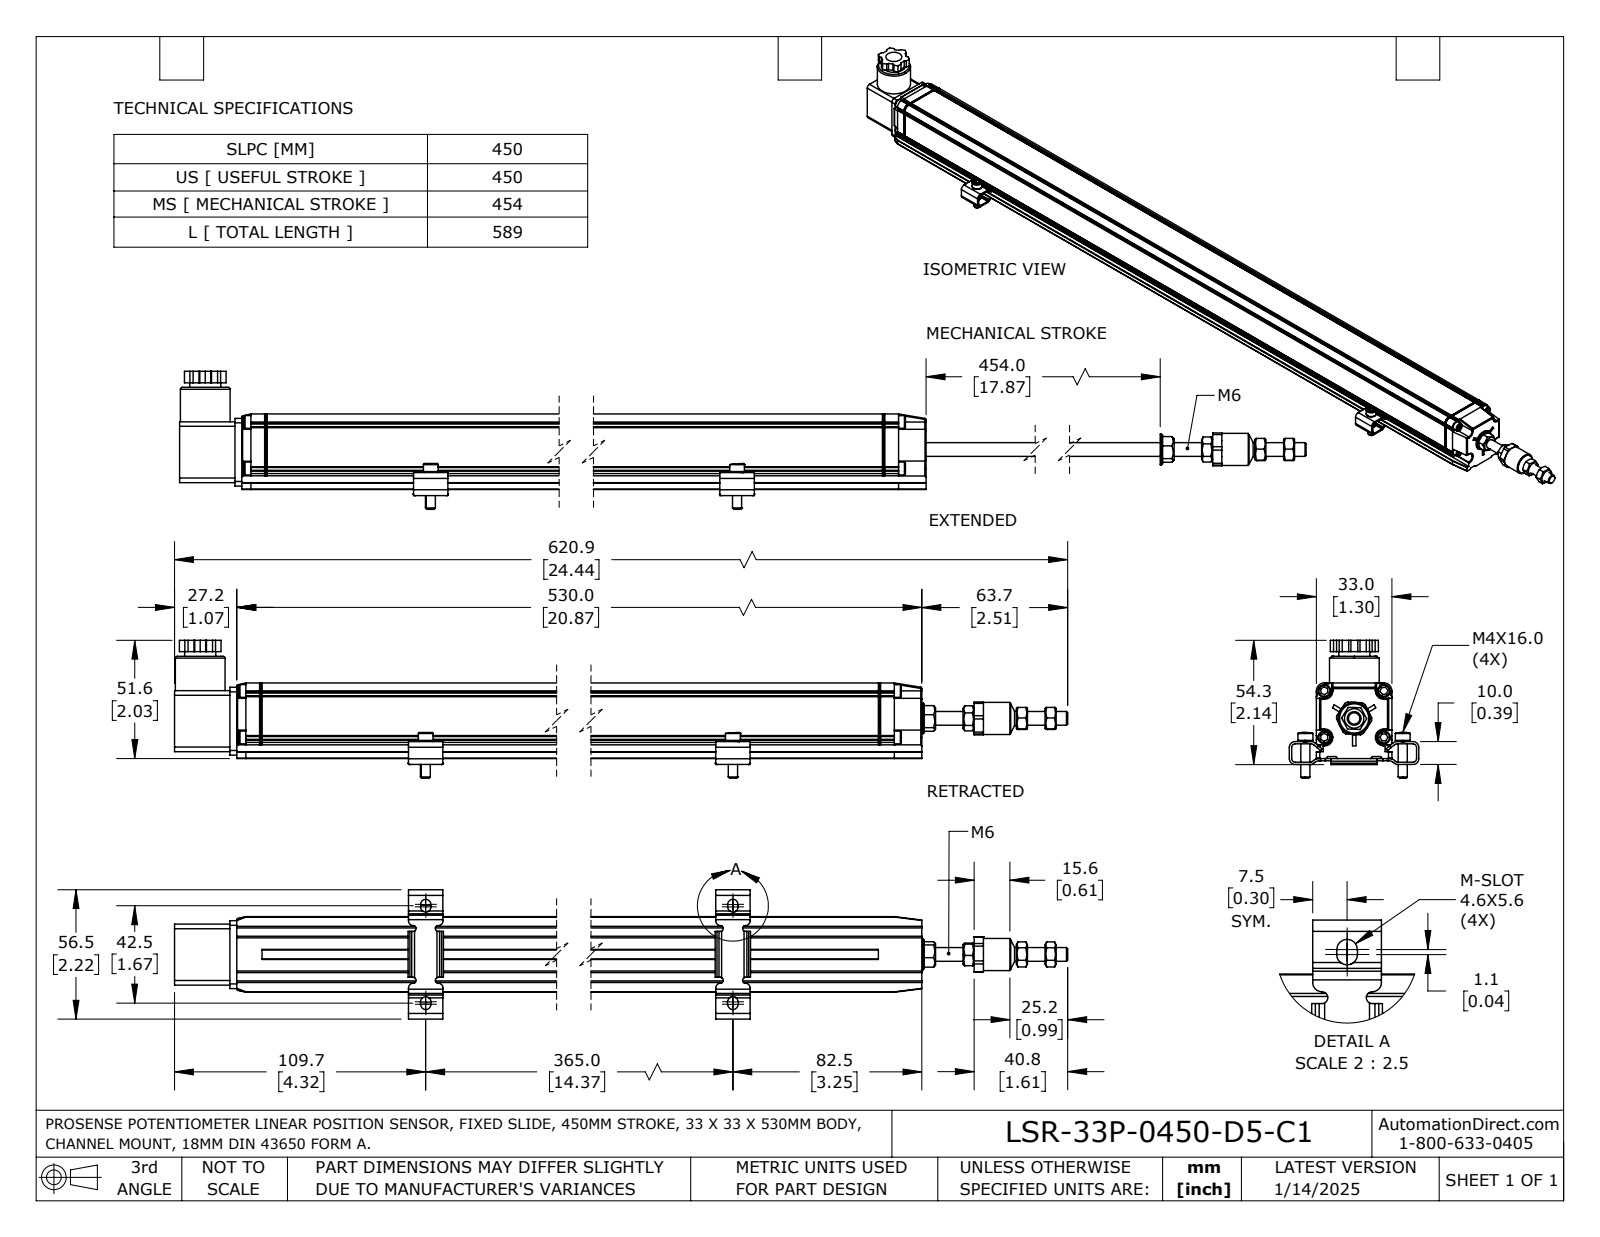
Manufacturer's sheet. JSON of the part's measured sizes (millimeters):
{"part_name": "LSR-33P-0450-D5-C1", "step_written_by": "SolidWorks 2023 (AUTOMOTIVE_DESIGN)", "units": "millimeters", "bodies": {"solids": 14, "faces": 995, "planar": 641, "cylindrical": 269, "other": 85}, "overall_size": [620.9, 60.2, 56.5], "volume_mm3": 538800, "surface_area_mm2": 135200, "round_holes": [[2.7, 4], [3.3, 4], [4.3, 1], [5.2, 1], [5.3, 1], [5.9, 1], [7, 1], [7.2, 1], [10, 1], [10.5, 1], [14.6, 1], [15.3, 1]], "round_bosses_or_shafts": [[4, 5], [3, 5], [6.5, 4], [5.6, 4], [21.7, 1], [14, 1], [13.6, 1], [13.4, 1]], "partial_cylinders_radius": [[2, 28], [0.5, 23], [0.2, 16], [1.3, 8], [1.5, 8], [2.3, 8], [3, 8], [1, 4]], "face_to_face_distances": [33, 3, 5.6, 30, 27.4, 1, 2, 3.6, 2.6, 4.7], "hole_center_spacings": [1.2, 14.8, 15.4, 17.7, 18.5, 20.3, 26, 33]}
